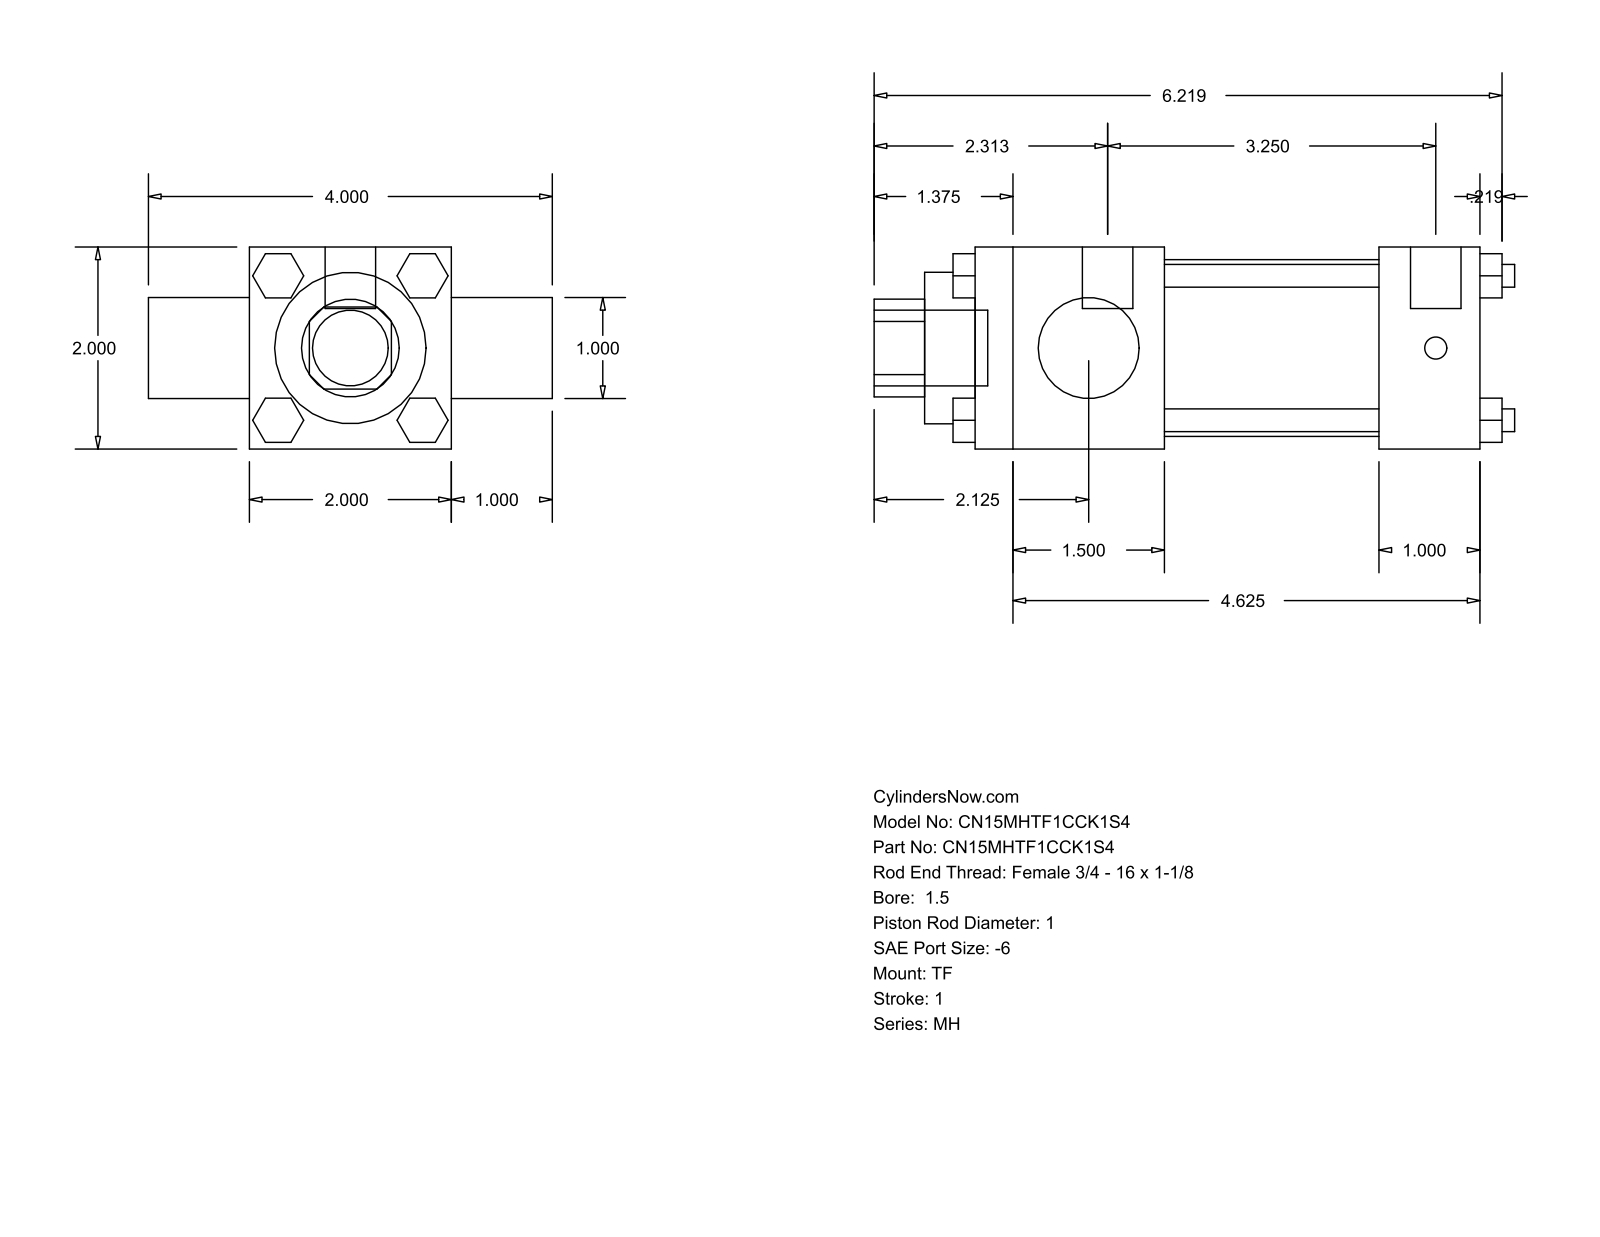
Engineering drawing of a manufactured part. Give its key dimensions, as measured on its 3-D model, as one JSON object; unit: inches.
{"part_name": "MH_TF__0150_1", "step_written_by": "GSSL Pune (CONFIG_CONTROL_DESIGN)", "units": "inches", "bodies": {"solids": 0, "faces": 120, "planar": 92, "cylindrical": 28, "other": 0}, "overall_size": [6.344, 4, 2], "round_holes": [[1, 2], [1.5, 1], [1.75, 1]], "round_bosses_or_shafts": [[0.225, 4], [0.219, 3], [0.5, 2], [0.75, 1]], "partial_cylinders_radius": [[0.484, 1]], "face_to_face_distances": [2, 1, 4, 5, 3, 1.875, 3.125, 2.125, 5.219, 0.5]}
